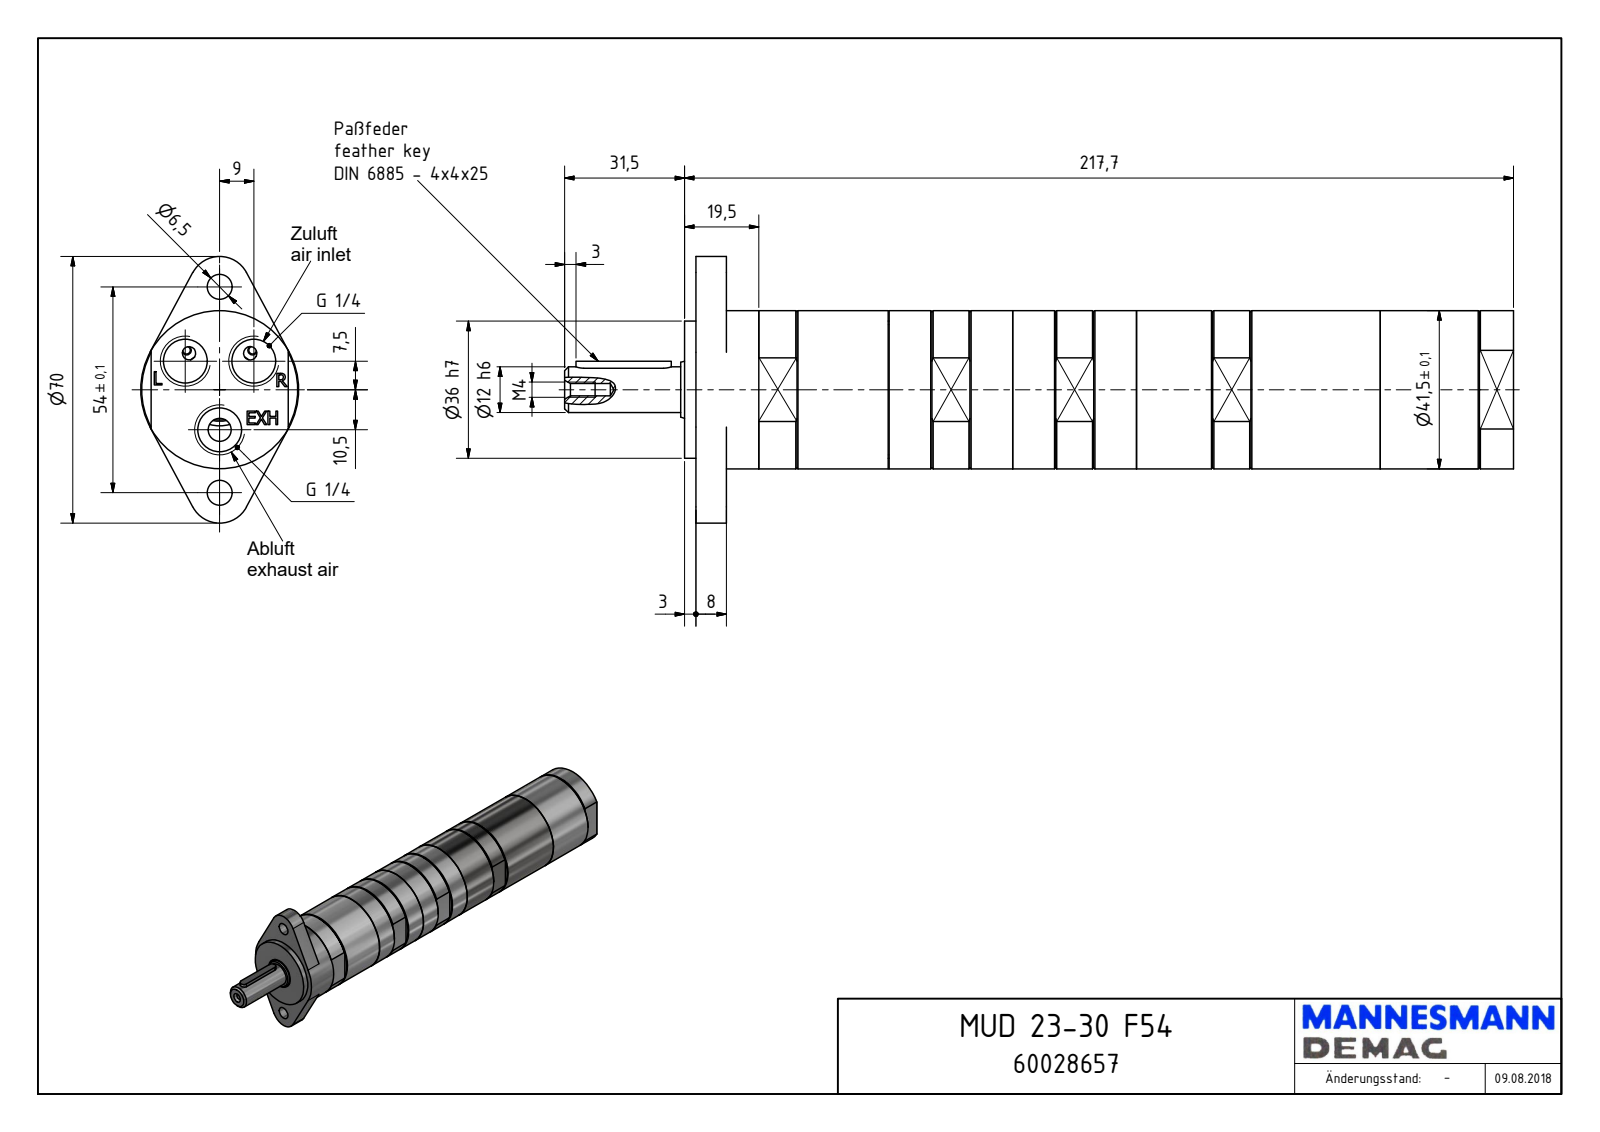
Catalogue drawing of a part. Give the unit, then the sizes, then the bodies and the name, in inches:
Units: inches
Overall size (bounding box): 9.811 × 2.756 × 1.634
Round holes (diameter × count): ⌀0.451 ×3, ⌀0.256 ×2, ⌀0.128 ×1, ⌀0.63 ×1
Round bosses / shafts (diameter × count): ⌀1.634 ×1, ⌀1.496 ×1, ⌀1.417 ×1, ⌀0.589 ×1, ⌀0.472 ×1, ⌀0.465 ×1
Partial cylindrical surfaces — rounded edges, fillets, slot ends (radius × count): R0.079 ×2, R0.315 ×2
Main face-to-face distances: 8.453, 0.118, 8.571, 1.496, 0.394, 0.433, 0.315, 8.138, 7.744, 0.039
Hole centre spacings: 0.461, 0.792, 0.846, 1.063, 1.404, 0.413, 0.65, 0.709
Volume: 18.04 in³ · Surface area: 56.38 in²
Bodies: 1 solid, 184 faces (107 planar, 36 cylindrical, 41 other)
Part name (STEP PRODUCT): MUD 23-30 F54_60028657
STEP written by: Autodesk Inventor 2024 (AUTOMOTIVE_DESIGN)
